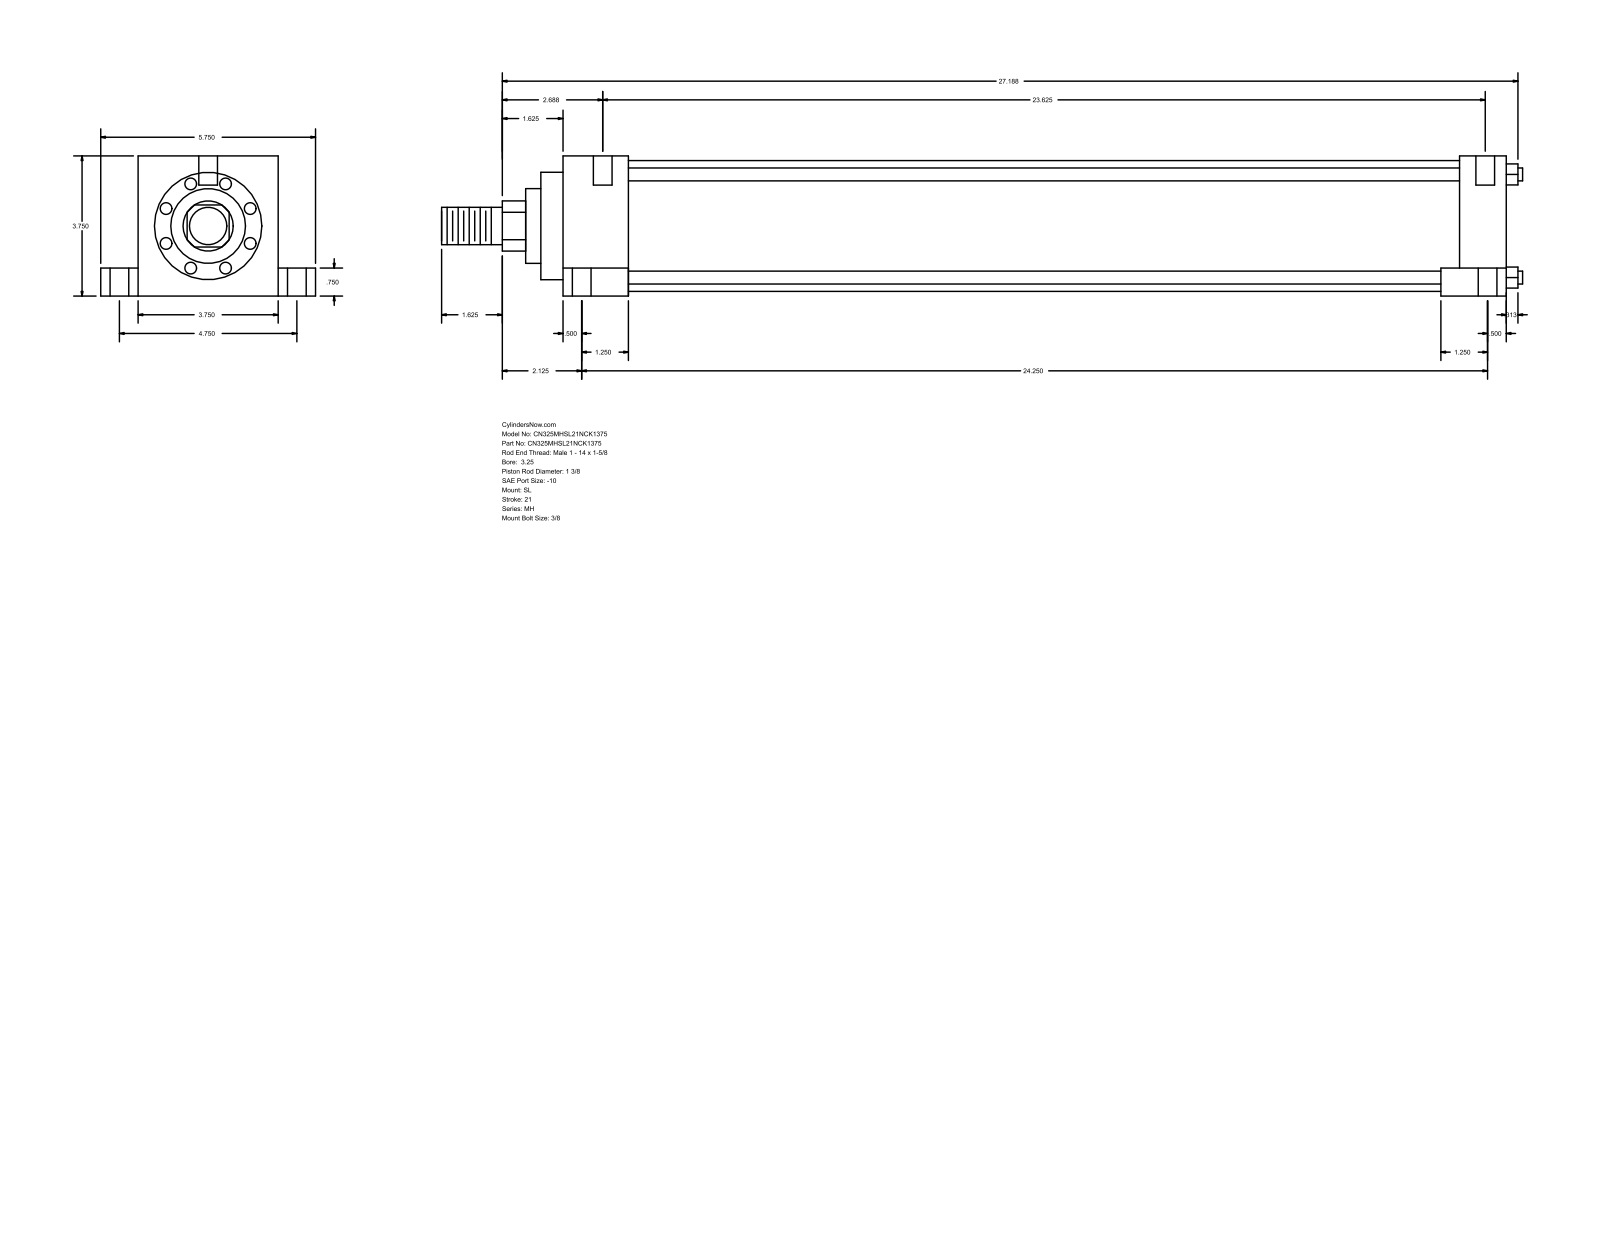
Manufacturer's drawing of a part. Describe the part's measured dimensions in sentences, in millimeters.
The part is named "MH_SL__0325_1.375". Its 3-D file was written by "GSSL Pune (CONFIG_CONTROL_DESIGN)". It is 0 solids with 110 faces: 77 planar, 33 cylindrical and 0 other. Overall it measures 735.01 by 146.05 by 95.25 millimeters. Round holes: 6 of diameter 12.7, 4 of diameter 5.56, 4 of diameter 19.05. Round bosses or shafts: 4 of diameter 8.76, 1 of diameter 88.9, 1 of diameter 73.03, 1 of diameter 50.8, 1 of diameter 34.92, 1 of diameter 25.4. Partial cylindrical surfaces (rounded edges, fillets, slot ends): 1 of radius 17.06. The main face-to-face distances are 95.24, 641.35, 44.45, 596.9, 25.41, 120.65, 19.05, 76.19, 609.61, 565.16. The hole center spacings are 60.35, 60.41, 61.65, 62, 120.66, 604.68, 606.26, 606.43.
